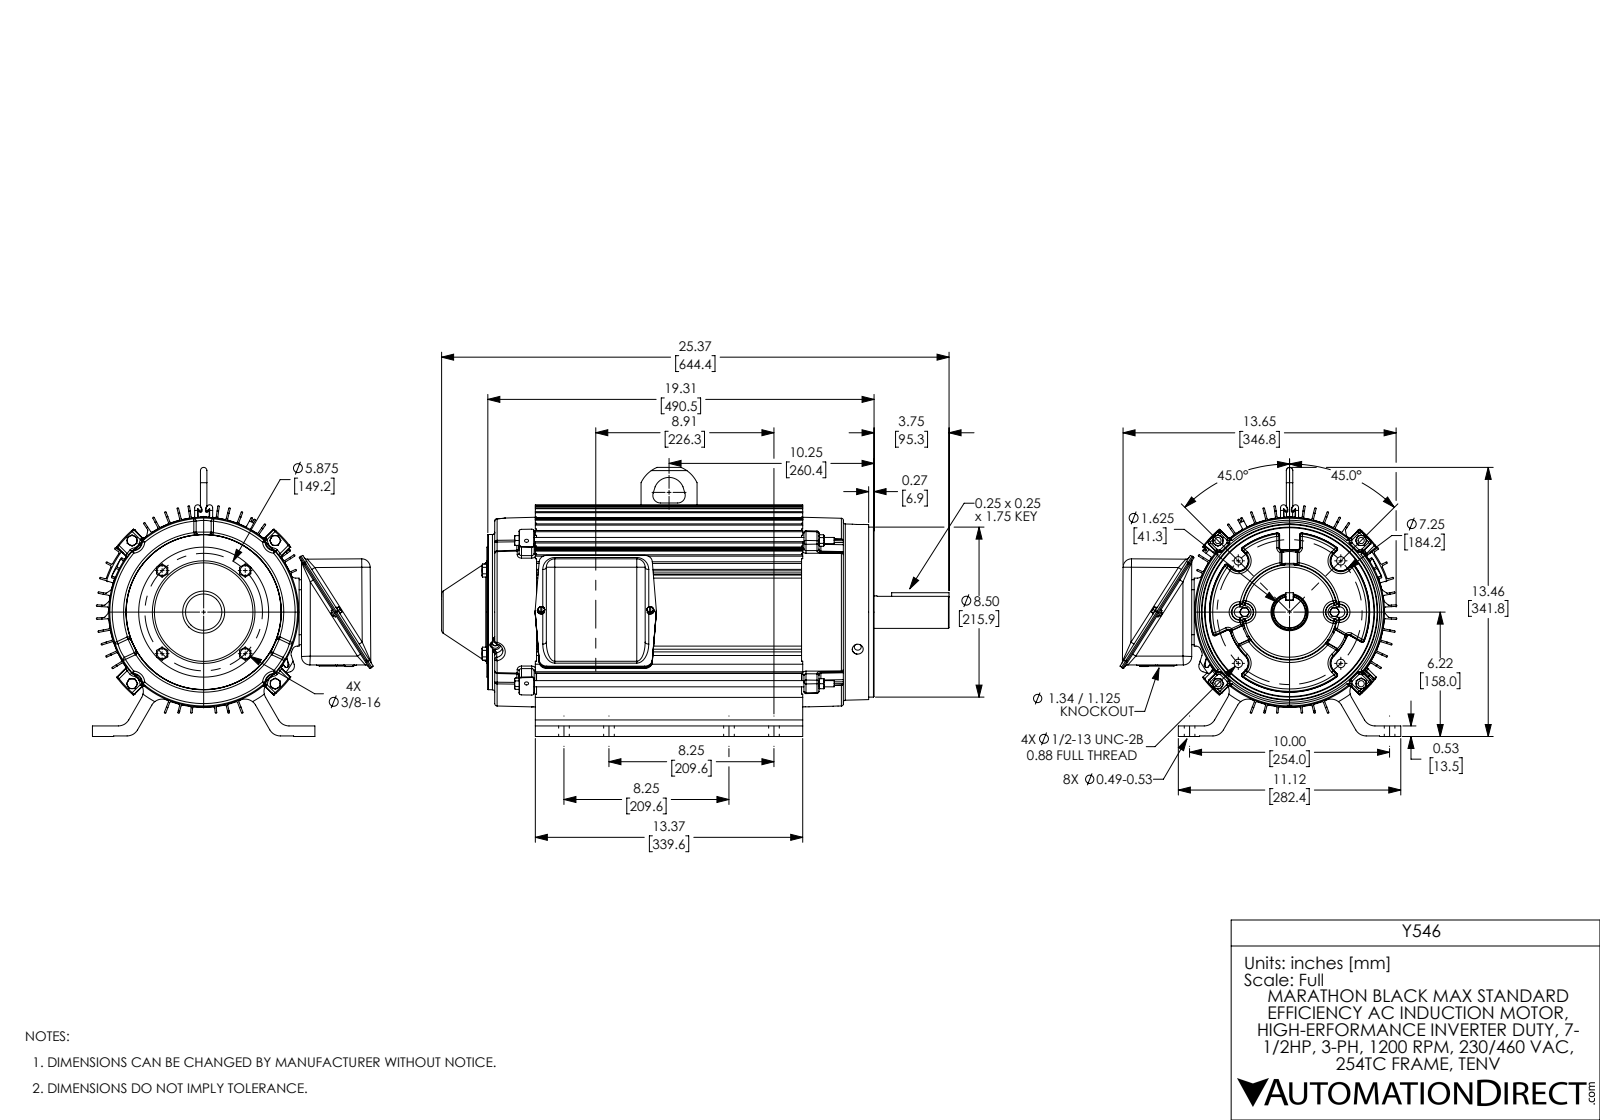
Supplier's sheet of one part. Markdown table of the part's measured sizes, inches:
| quantity | value |
| --- | --- |
| part name | SS330123-1325_Rev3 r1 |
| STEP written by | SolidWorks 2017 (AUTOMOTIVE_DESIGN) |
| units | inches |
| bodies | 30 solids, 2963 faces (688 planar, 952 cylindrical, 1323 other) |
| overall size | 25.372 × 14.038 × 13.456 |
| volume | 370.7 in³ |
| surface area | 3 023 in² |
| round holes (diameter × count) | 0.343 × 10, 0.531 × 8, 0.25 × 5, 0.5 × 5, 0.201 × 4, 0.257 × 4, 0.312 × 4, 0.406 × 4, 0.421 × 4, 0.44 × 4, 0.176 × 2, 0.199 × 2 |
| round bosses / shafts (diameter × count) | 0.5 × 4, 0.375 × 4, 0.31 × 4, 0.38 × 3, 0.399 × 2, 0.33 × 2, 0.25 × 2, 0.19 × 2 |
| partial cylindrical surfaces (radius × count) | 0.12 × 130, 0.06 × 80, 0.1 × 54, 0.038 × 32, 0.38 × 29, 0.03 × 15, 0.18 × 12, 0.095 × 8 |
| main face-to-face distances | 0.076, 0.06, 17.576, 0.63, 0.53, 0.076, 0.12, 0.03, 0.2, 17.776 |
| hole center spacings | 4.666, 5.851, 5.853, 6.224, 6.227, 7.158, 2.25, 0.03 |
